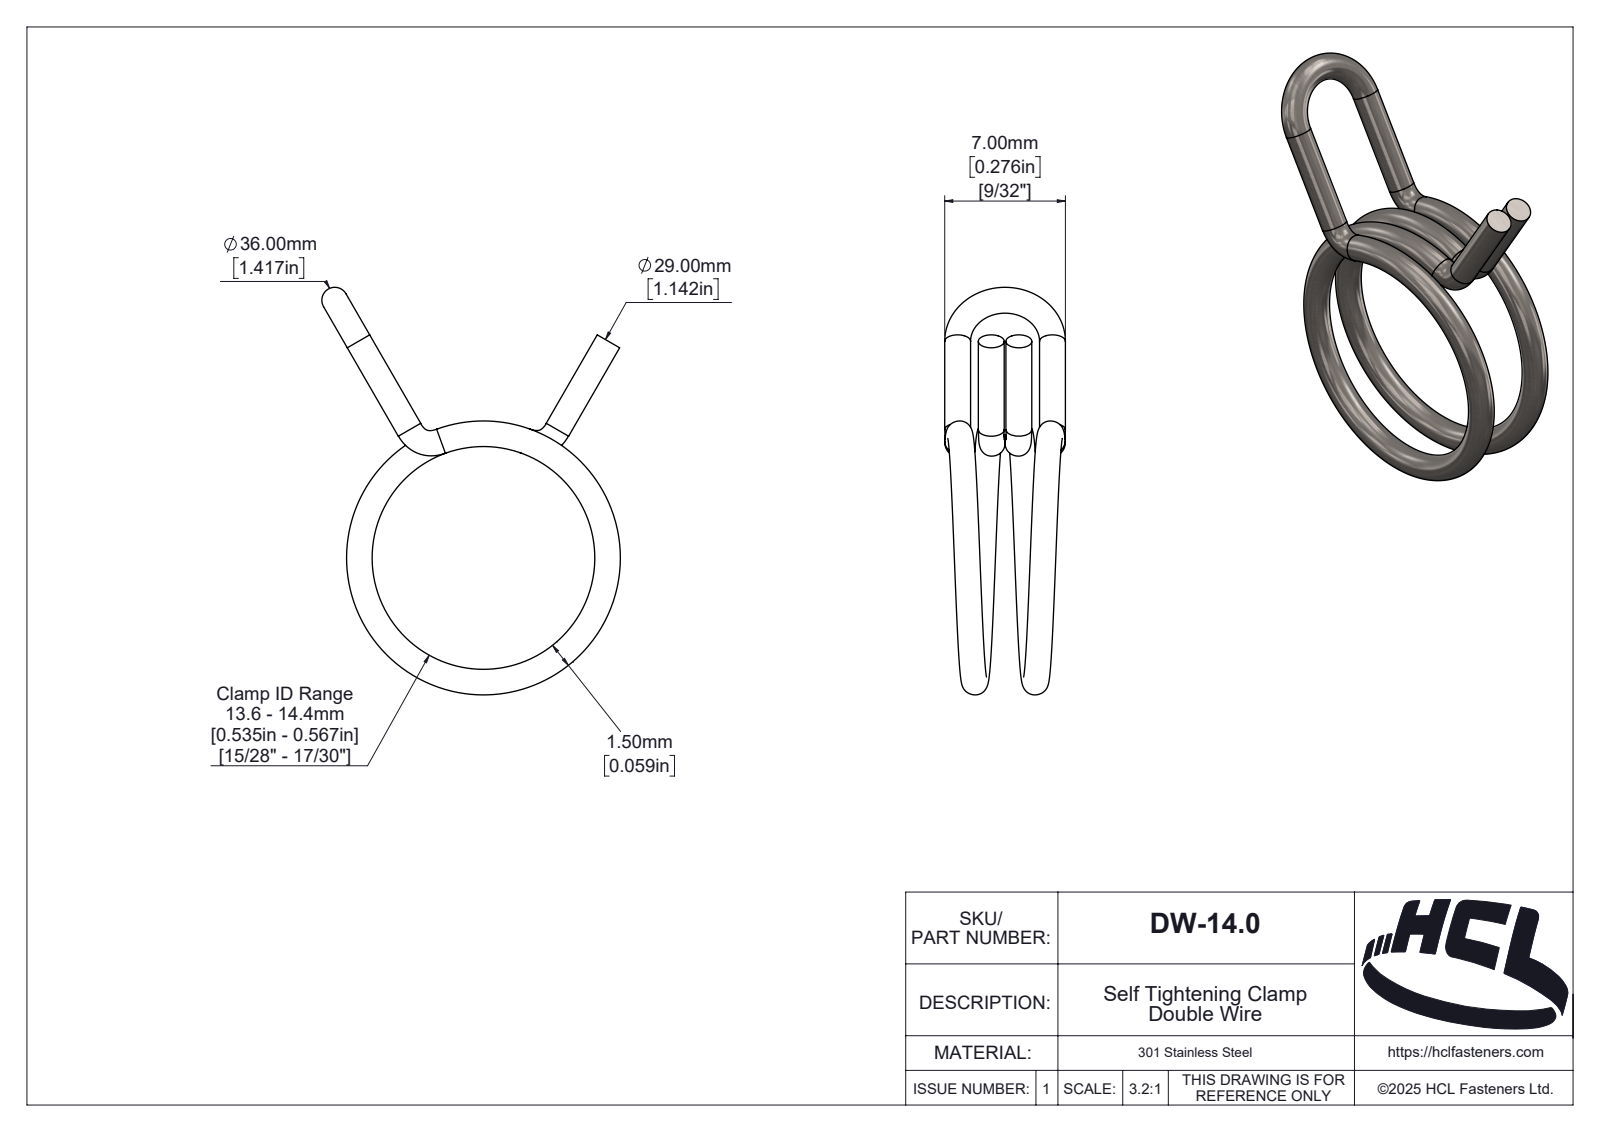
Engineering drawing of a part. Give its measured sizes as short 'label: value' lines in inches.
name: DW-14.0
written by: SolidWorks 2025 (AUTOMOTIVE_DESIGN)
unit: in
bodies: 1 solid, 132 faces (14 planar, 53 cylindrical, 65 other)
size: 0.93 × 0.682 × 0.276
volume: 0.015 in³; area: 1.03 in²
bosses: 4× ⌀0.059
rounds: 1× R0.006, 1× R0.008, 1× R0.008, 1× R0.01, 1× R0.014, 1× R0.019, 1× R0.024, 1× R0.027
